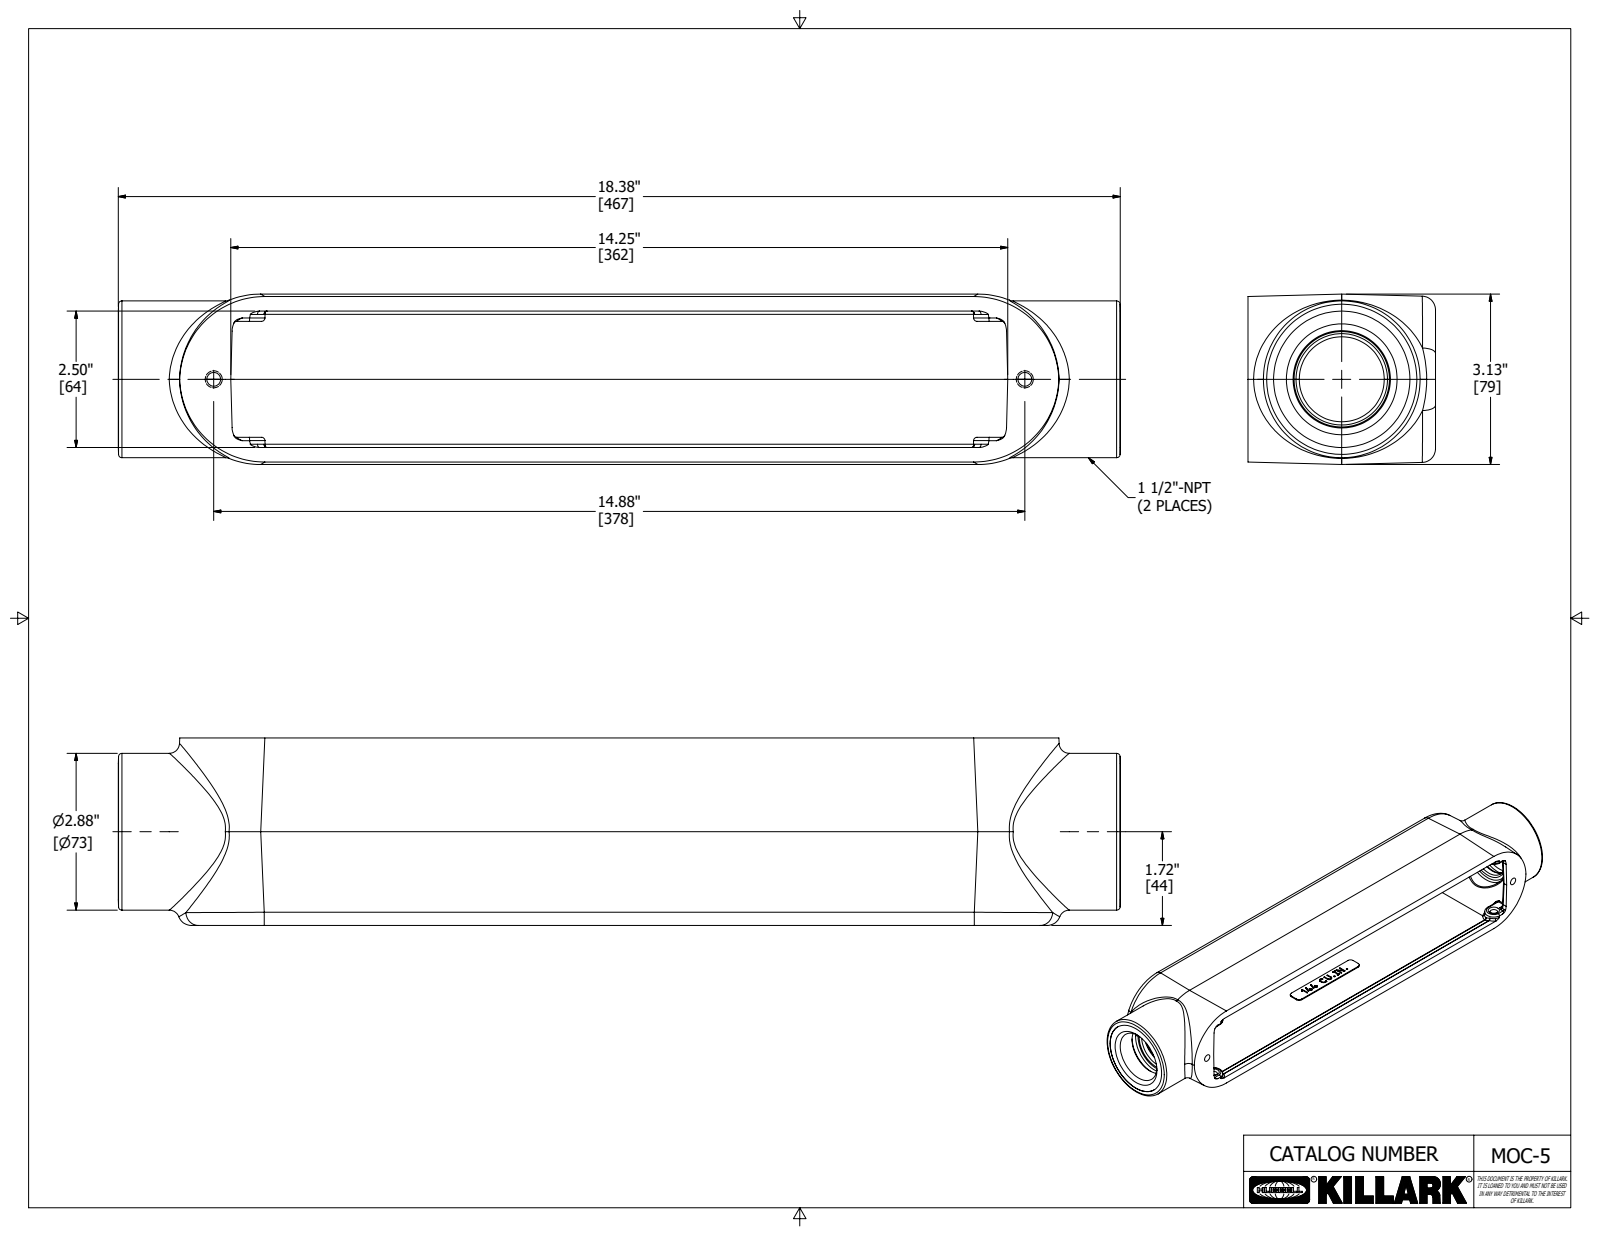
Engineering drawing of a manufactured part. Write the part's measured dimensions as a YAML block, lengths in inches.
part_name: "21236-2"
step_written_by: "Autodesk Inventor 2020 (AUTOMOTIVE_DESIGN)"
units: inches
bodies: {solids: 1, faces: 661, planar: 282, cylindrical: 71, other: 308}
overall_size: [18.375, 3.438, 3.125]
volume: 48.45
surface_area: 362
round_holes:
  - {diameter: 0.252, count: 2}
  - {diameter: 1.558, count: 1}
  - {diameter: 1.906, count: 1}
  - {diameter: 2, count: 1}
round_bosses_or_shafts:
  - {diameter: 2.875, count: 1}
partial_cylinders:
  - {radius: 0.062, count: 20}
  - {radius: 1.563, count: 8}
  - {radius: 0.062, count: 6}
  - {radius: 0.125, count: 6}
  - {radius: 0.375, count: 4}
  - {radius: 1.25, count: 4}
  - {radius: 0.25, count: 2}
  - {radius: 0.005, count: 1}
face_to_face_distances: [3.125, 2.625, 3.438, 0.063, 2.563, 0.031, 3.406, 2.5, 3, 0.031]
hole_center_spacings: [14.875]
